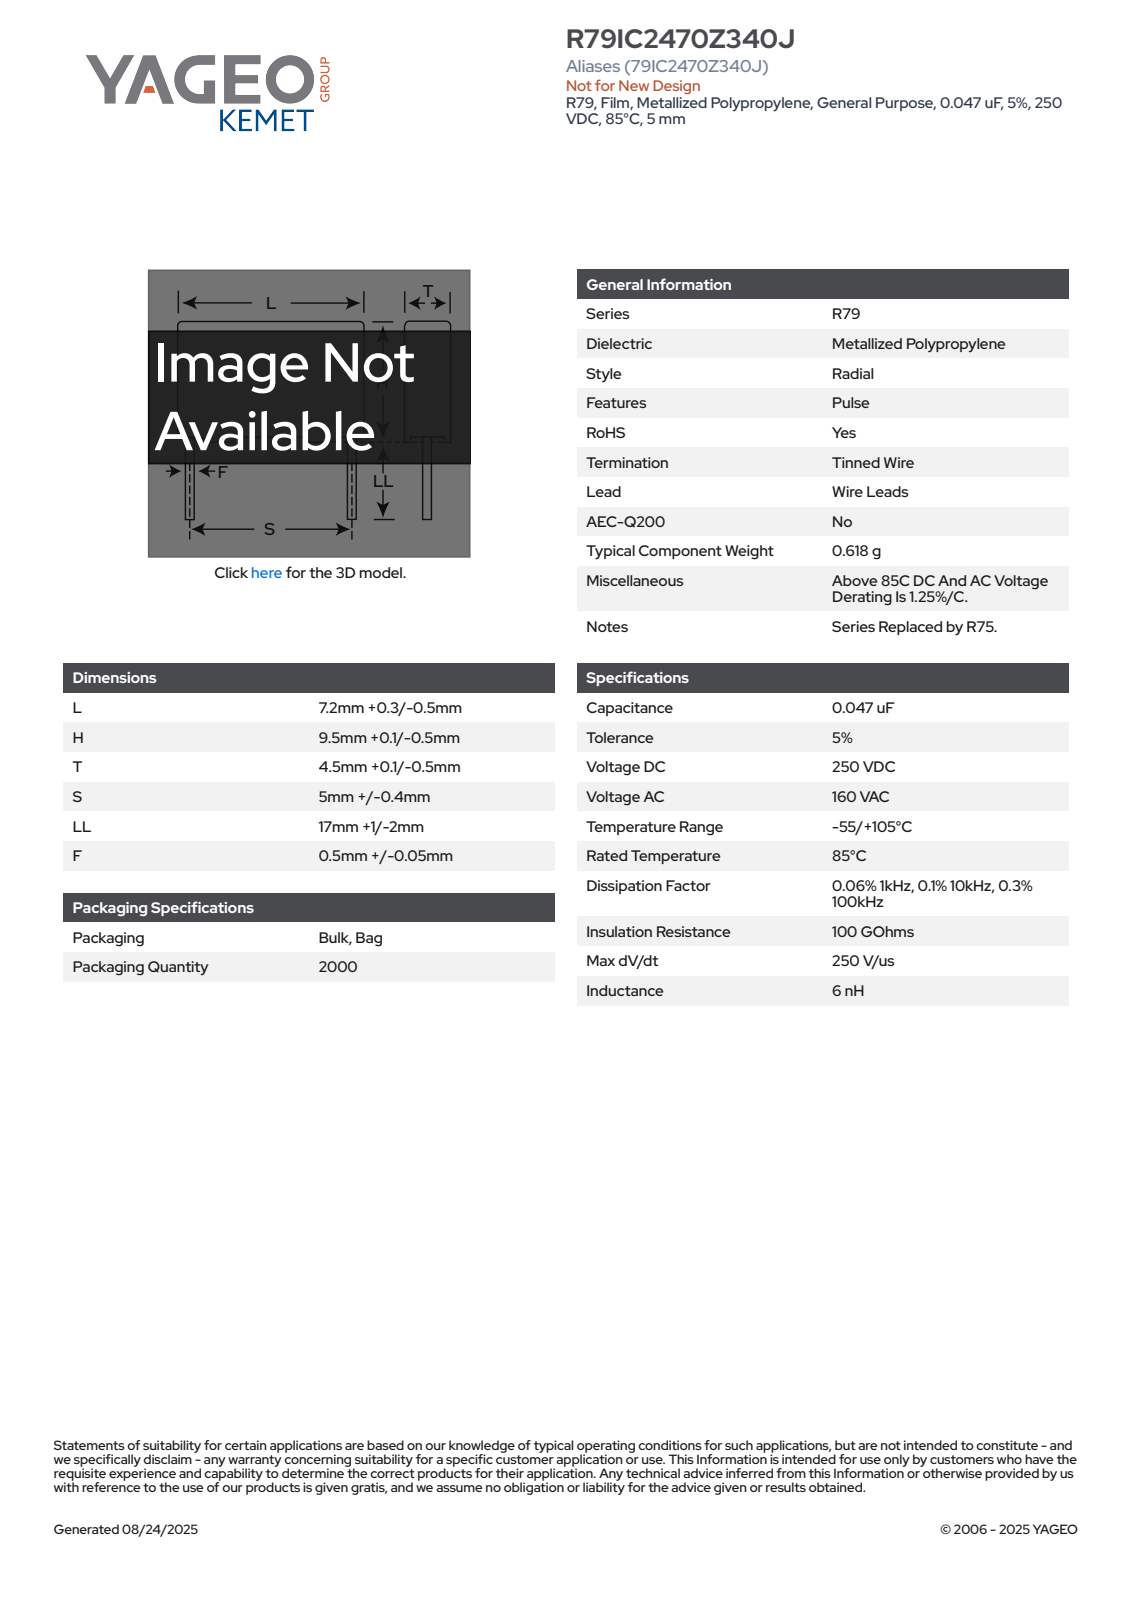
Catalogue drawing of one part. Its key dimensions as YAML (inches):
part_name: "CFR_RB2_7.2X9.5X4.5_L7.5H9.6T4.6S5LL18F0.55"
step_written_by: "SolidWorks 2021 (AUTOMOTIVE_DESIGN)"
units: inches
bodies: {solids: 4, faces: 85, planar: 77, cylindrical: 8, other: 0}
overall_size: [1.087, 0.295, 0.181]
volume: 0.019
surface_area: 0.589
round_bosses_or_shafts:
  - {diameter: 0.022, count: 2}
partial_cylinders:
  - {radius: 0.02, count: 4}
face_to_face_distances: [0.181, 0.295, 0.348, 0.171, 0.285, 0.03, 0.378, 0.161, 0.276, 0.013]
